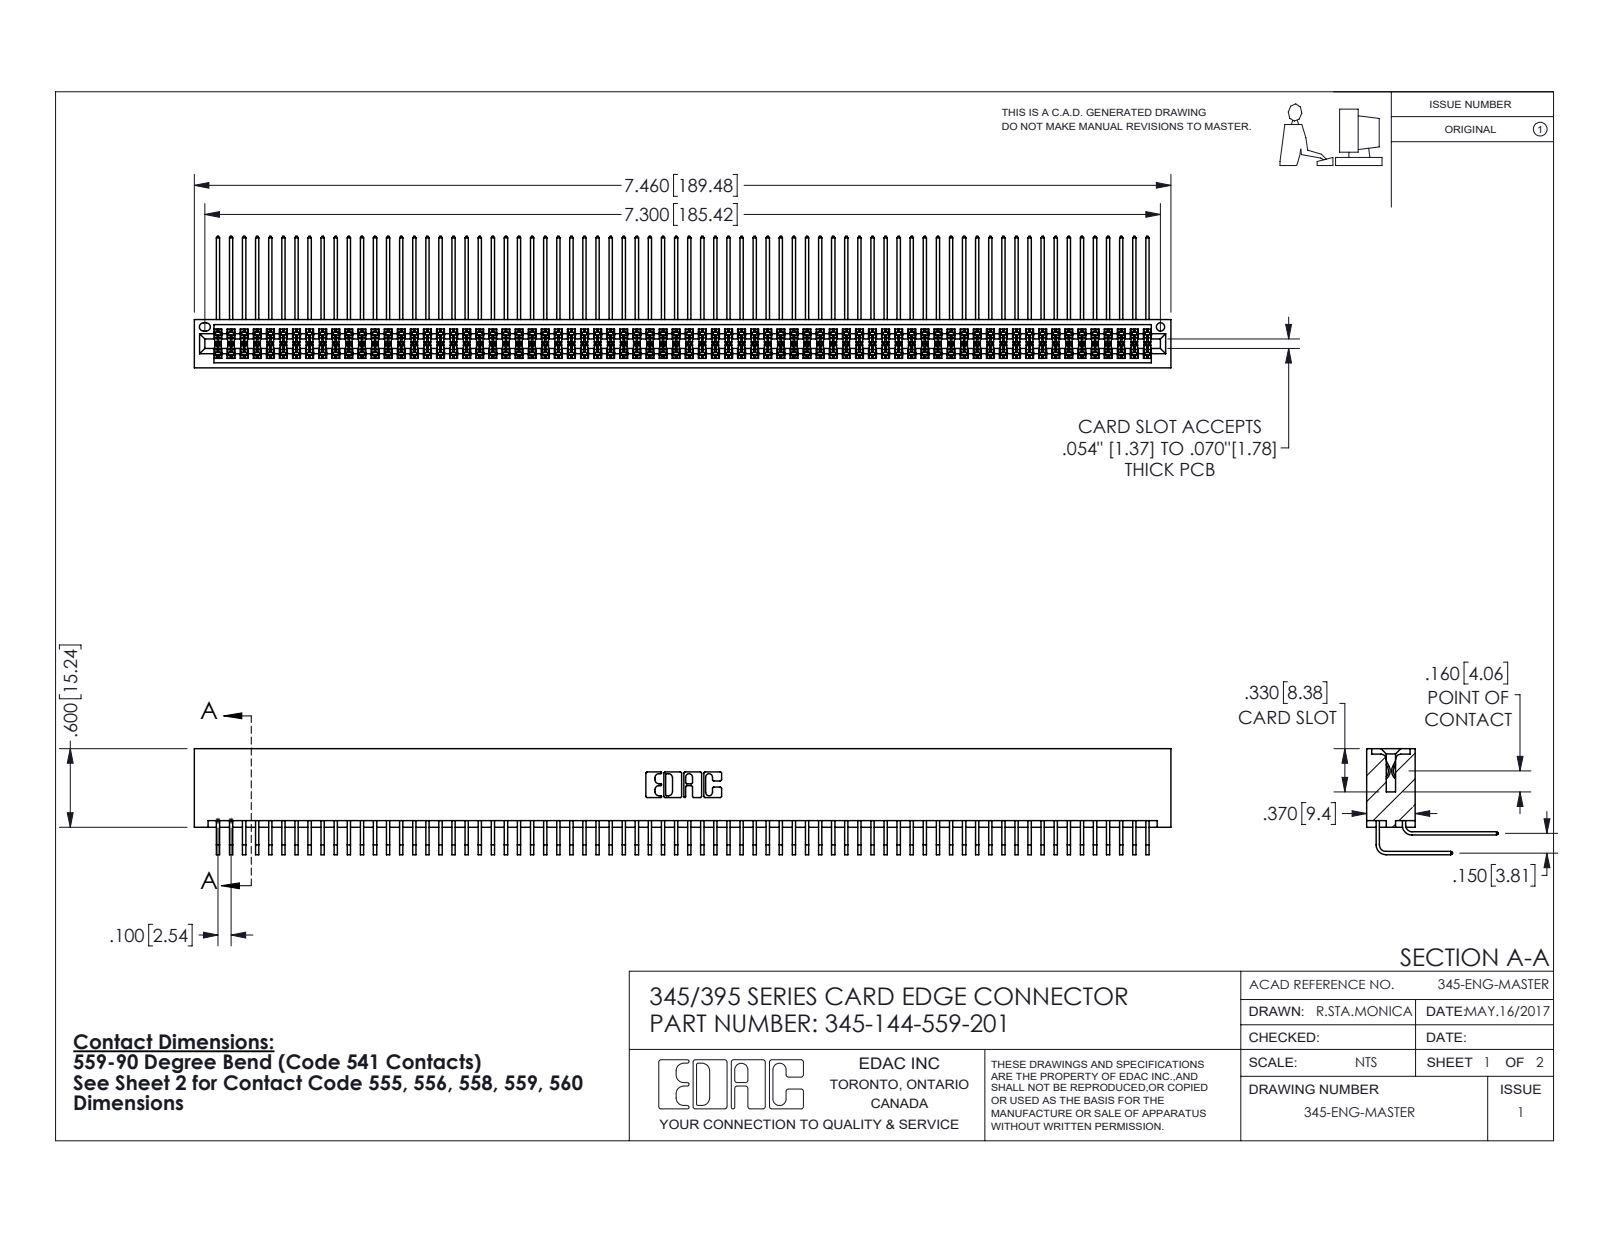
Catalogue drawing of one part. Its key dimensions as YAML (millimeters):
part_name: "345 Part_No Mounting Lugs; 345-144-559-201; 345-292-001_559 Tail - 2; 345-292-001_558 559 Tail - 1"
step_written_by: "SolidWorks 2016 (CONFIG_CONTROL_DESIGN)"
units: millimeters
bodies: {solids: 145, faces: 7606, planar: 5116, cylindrical: 2490, other: 0}
overall_size: [189.5, 25.5, 20.5]
volume: 20140
surface_area: 34550
round_holes:
  - {diameter: 1.6, count: 1}
partial_cylinders:
  - {radius: 0.2, count: 217}
  - {radius: 0.3, count: 22}
  - {radius: 0.2, count: 6}
  - {radius: 0.8, count: 6}
  - {radius: 0.7, count: 3}
  - {radius: 0.4, count: 2}
  - {radius: 0.5, count: 2}
  - {radius: 0.6, count: 2}
face_to_face_distances: [1.8, 7.6, 5.1, 9.4, 2.5, 6.9, 0.6, 5.7, 4.4, 3.8]
